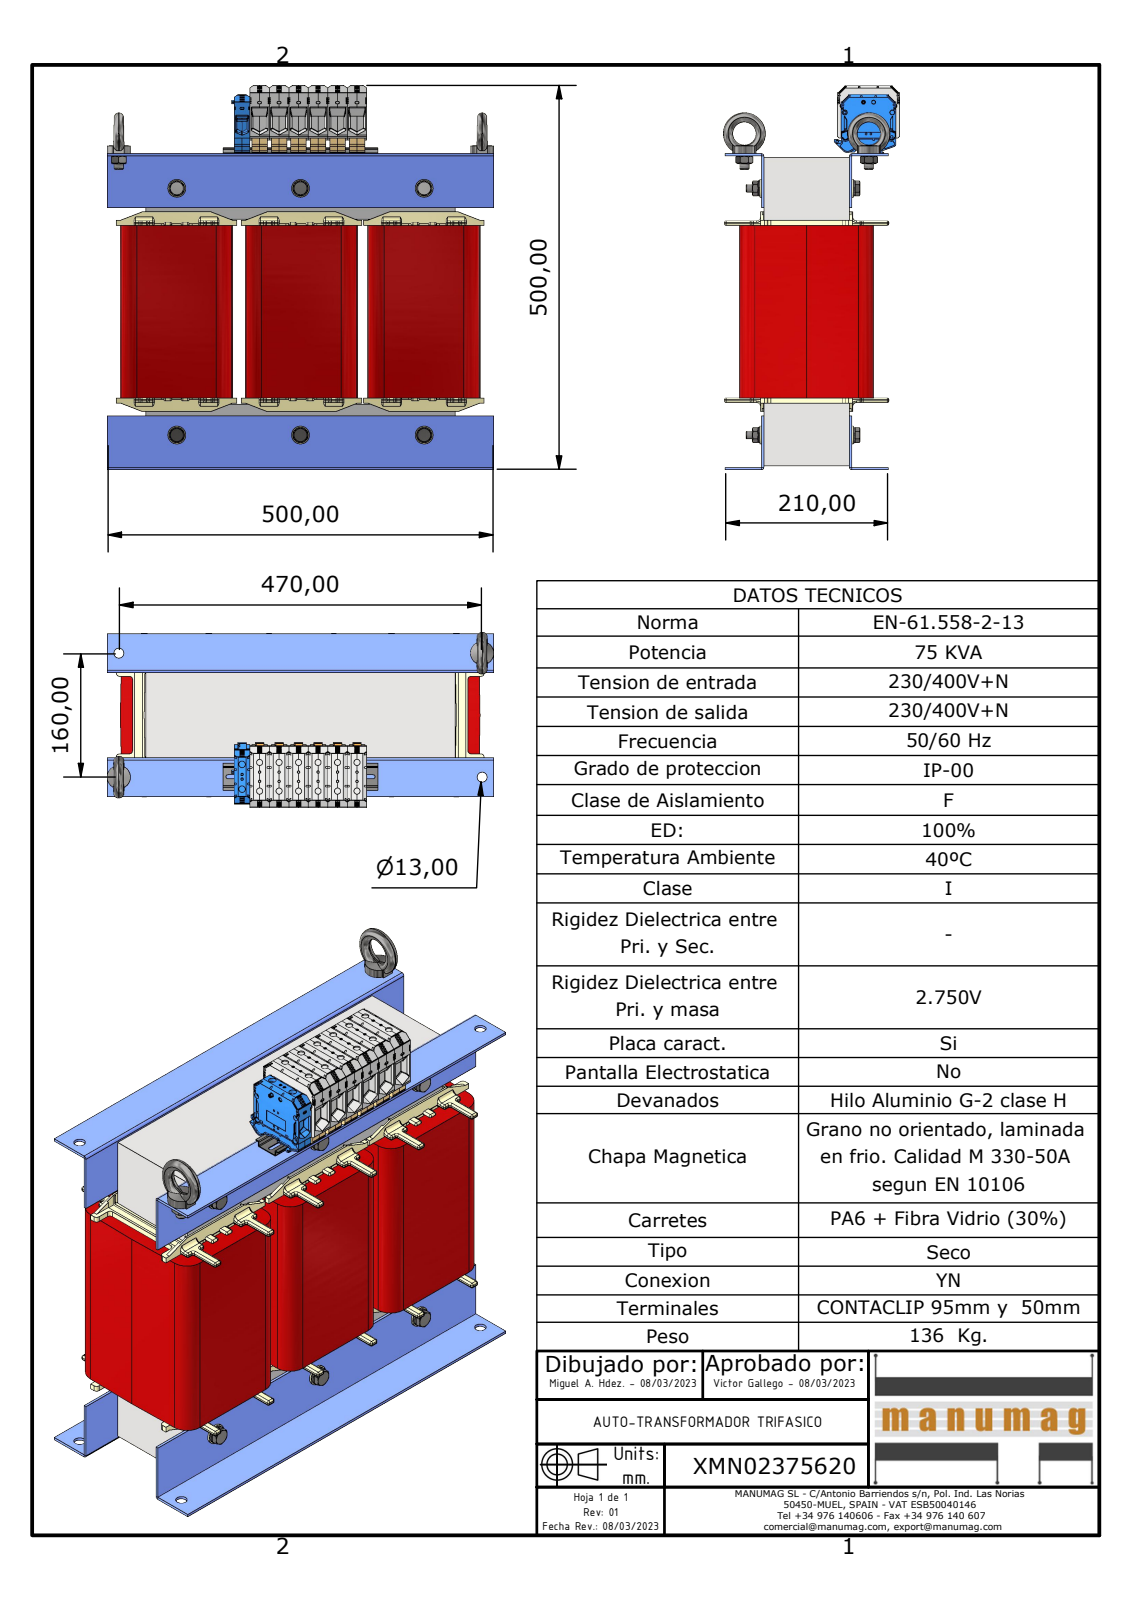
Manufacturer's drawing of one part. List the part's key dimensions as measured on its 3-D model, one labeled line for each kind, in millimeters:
Part name (STEP PRODUCT): XMN02375620; 3UI240 400 x 400 - 110; UI 240_110_BOBINADO; RC80 NT080 (+8 more)
STEP written by: Autodesk Inventor 2023 (AUTOMOTIVE_DESIGN)
Units: millimetres
Bodies: 65 solids, 8882 faces (5041 planar, 2769 cylindrical, 1072 other)
Overall size (bounding box): 500 × 498.7 × 226.5
Volume: 25 040 000 mm³ · Surface area: 2 795 000 mm²
Round holes (diameter × count): ⌀2.75 ×14, ⌀2.95 ×14, ⌀2.5 ×12, ⌀8 ×12, ⌀13 ×10, ⌀8.38 ×6, ⌀10 ×6, ⌀10.5 ×6, ⌀15 ×6, ⌀3.4 ×4, ⌀6.5 ×4, ⌀8.5 ×2
Round bosses / shafts (diameter × count): ⌀0.6 ×12, ⌀23 ×6, ⌀20 ×6, ⌀15.4 ×6, ⌀11.5 ×6, ⌀9.19 ×6, ⌀54 ×2, ⌀12 ×2
Partial cylindrical surfaces — rounded edges, fillets, slot ends (radius × count): R1 ×286, R2 ×218, R0.3 ×207, R0.5 ×41, R0.81 ×33, R1.9 ×32, R0.3 ×26, R0.49 ×24
Main face-to-face distances: 3, 6, 320, 110, 24.85, 30.86, 2, 120.55, 113, 116
Hole centre spacings: 25.2, 28.13, 35.15, 50.4, 51.93, 56.04, 76.63, 12.5
